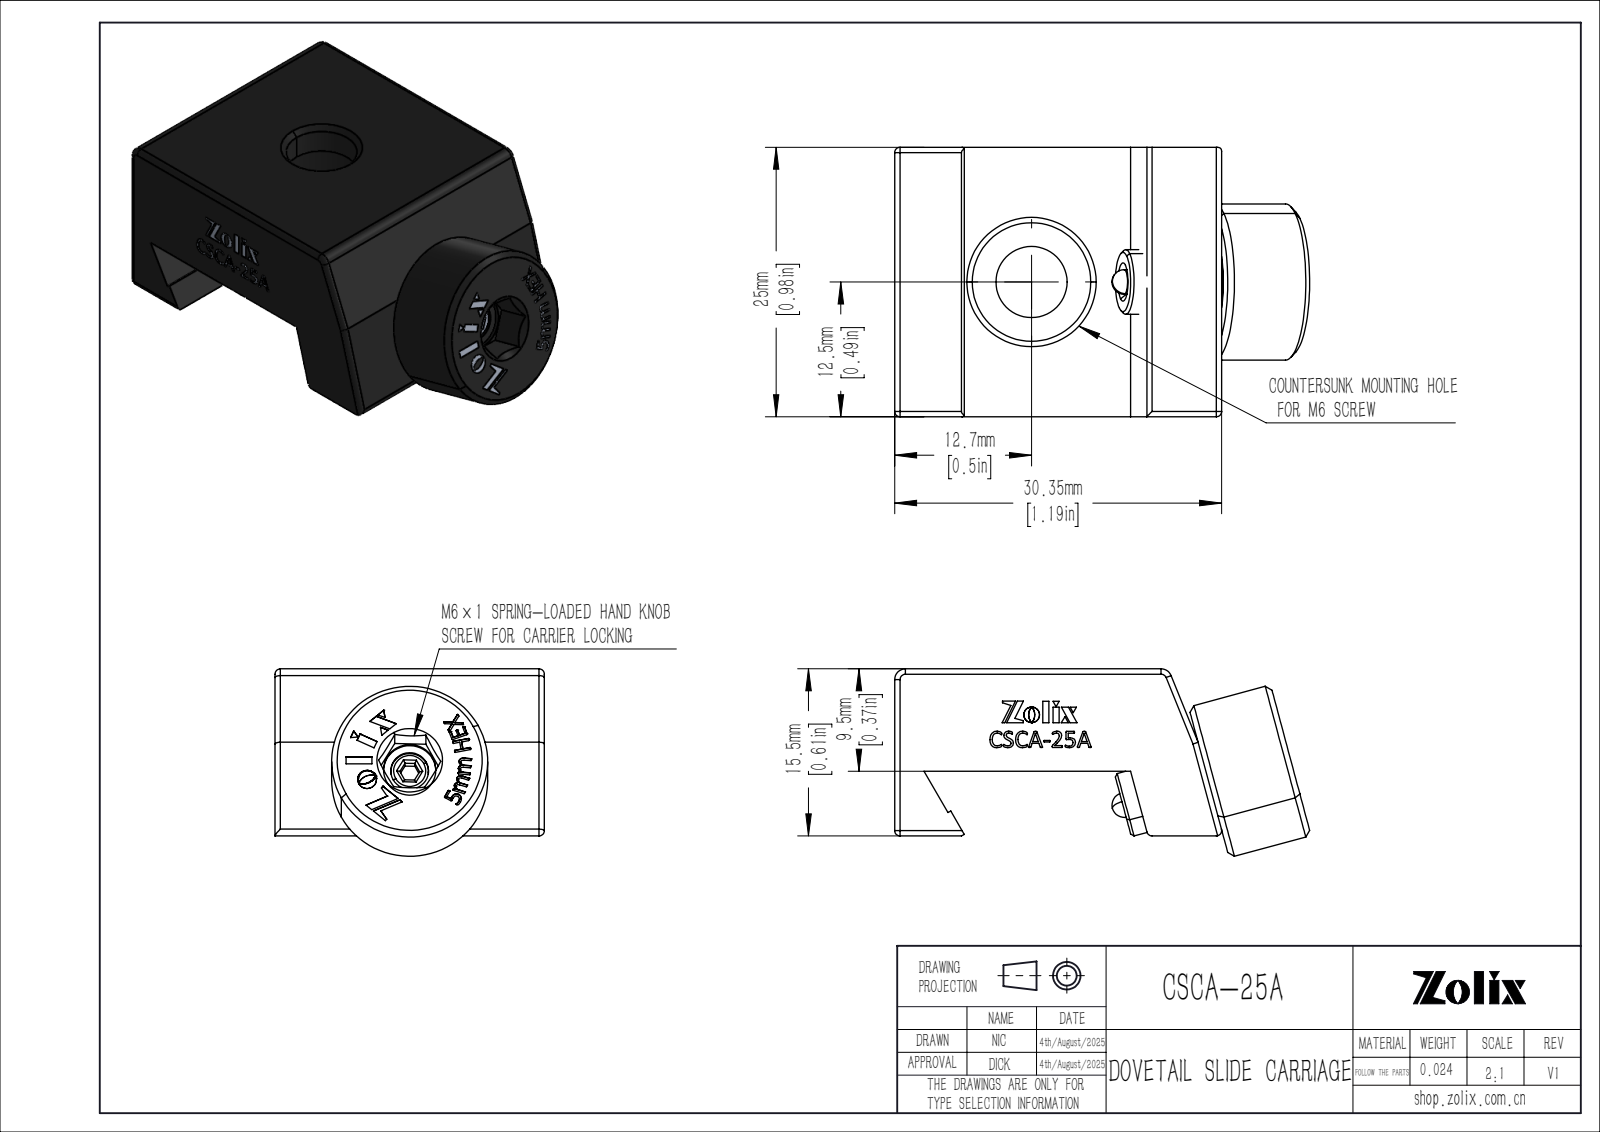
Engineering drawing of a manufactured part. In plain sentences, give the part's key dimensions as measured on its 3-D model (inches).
The part is named "CSCA-25A". Its 3-D file was written by "SolidWorks 2020 (AUTOMOTIVE_DESIGN)". It is 5 solids with 722 faces: 484 planar, 64 cylindrical and 174 other. Overall it measures 1.517 by 0.984 by 0.685 inches. Its volume is 0.531 cubic inches and its surface area 7.217 square inches. Round holes: 1 of diameter 0.085, 1 of diameter 0.1, 1 of diameter 0.125, 1 of diameter 0.138, 1 of diameter 0.191, 1 of diameter 0.197, 1 of diameter 0.26, 1 of diameter 0.405, 1 of diameter 0.433. Round bosses or shafts: 1 of diameter 0.57, 1 of diameter 0.395, 1 of diameter 0.236, 1 of diameter 0.137, 1 of diameter 0.118, 1 of diameter 0.09. Partial cylindrical surfaces (rounded edges, fillets, slot ends): 13 of radius 0.02, 2 of radius 0.039. The main face-to-face distances are 0.374, 0.984, 0.236, 0.61, 0.31, 0.106, 0.268, 0.504, 0.197, 0.15.
